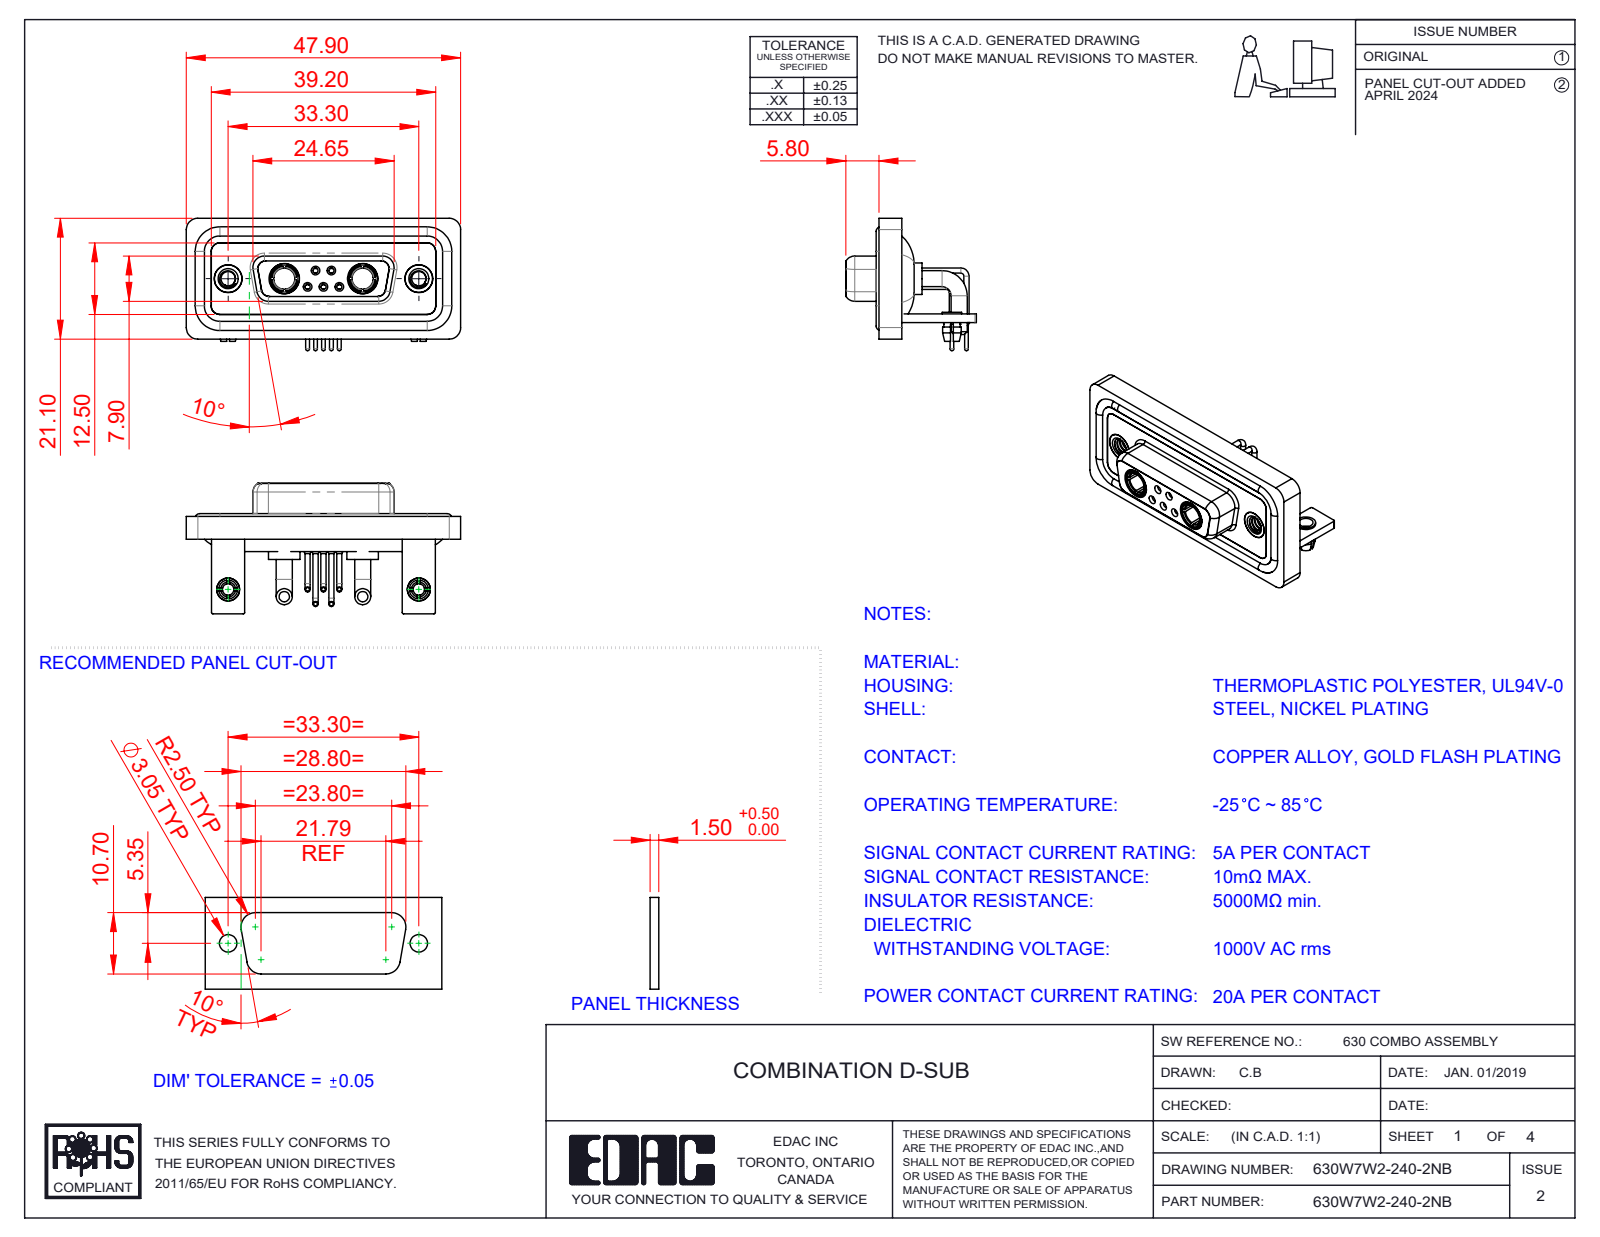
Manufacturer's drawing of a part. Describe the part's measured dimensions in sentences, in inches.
The part is named "630W7W2-240-2NB; 630Combo Waterproof Housing_15 Contacts; 630Combo Board Lock_50 Contacts; 630Combo Shell Rear_15 Contacts (+7 more)". Its 3-D file was written by "SolidWorks 2023 (CONFIG_CONTROL_DESIGN)". It is 20 solids with 941 faces: 306 planar, 407 cylindrical and 228 other. Overall it measures 1.886 by 0.91 by 0.898 inches. Its volume is 0.402 cubic inches and its surface area 17.29 square inches. Round holes: 7 of diameter 0.079, 5 of diameter 0.035, 5 of diameter 0.043, 5 of diameter 0.059, 4 of diameter 0.098, 4 of diameter 0.191, 3 of diameter 0.063, 2 of diameter 0.067, 2 of diameter 0.126, 2 of diameter 0.146, 2 of diameter 0.157, 2 of diameter 0.159. Round bosses or shafts: 6 of diameter 0.063, 5 of diameter 0.035, 5 of diameter 0.026, 4 of diameter 0.11, 2 of diameter 0.217, 2 of diameter 0.205, 2 of diameter 0.195, 2 of diameter 0.195. Partial cylindrical surfaces (rounded edges, fillets, slot ends): 21 of radius 0.079, 18 of radius 0.059, 16 of radius 0.01, 12 of radius 0.053, 8 of radius 0.063, 5 of radius 0.02, 4 of radius 0.024, 4 of radius 0.026. The main face-to-face distances are 0.016, 0.114, 0.059, 0.071, 0.146, 0.043, 0.161, 0.063, 0.098, 0.055. The hole center spacings are 0.124, 0.109, 0.386, 0.925, 1.311, 0.17, 0.17, 0.198.
